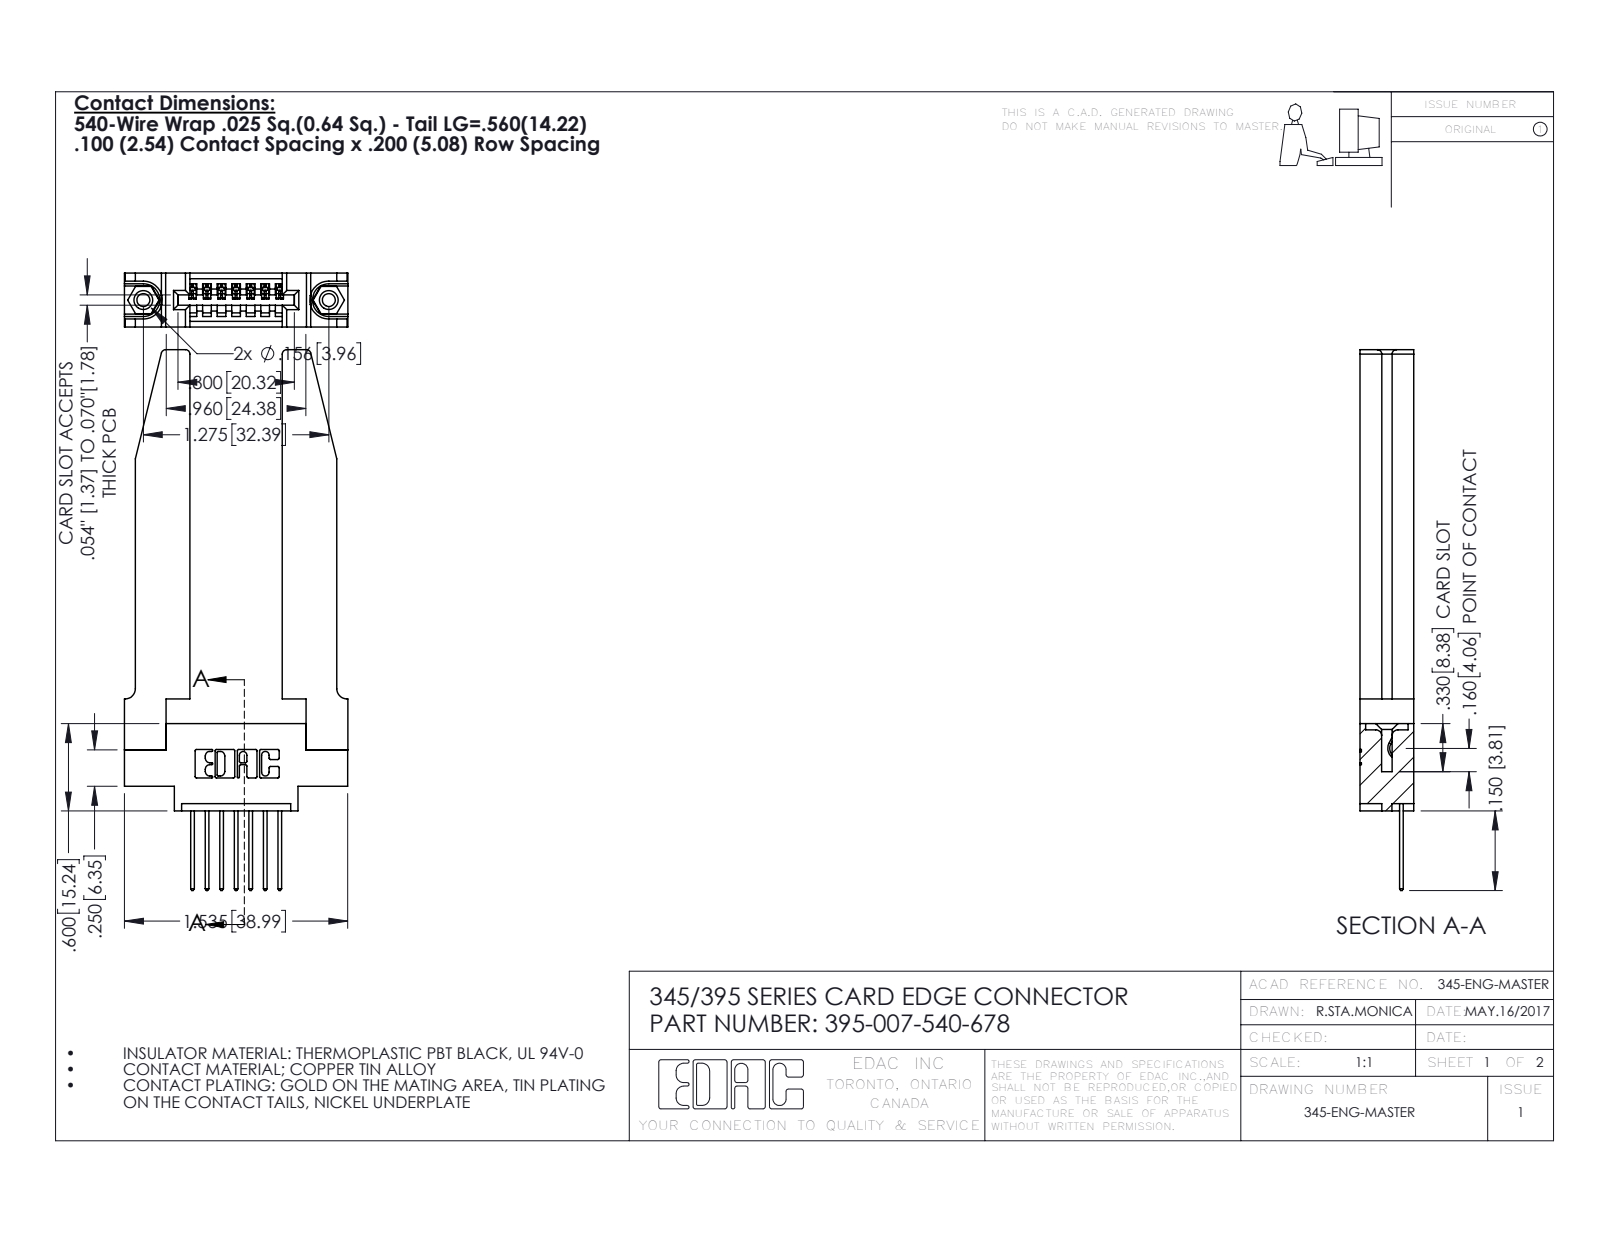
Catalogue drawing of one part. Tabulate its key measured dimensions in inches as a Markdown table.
| quantity | value |
| --- | --- |
| part name | 345-250-001_345-250-001-102; 345-292-001_345-293-140; 345-220-078_345-220-078; 345 Part_0.170 Offset - 0.156 Dia-TH (+1 more) |
| STEP written by | SolidWorks 2016 (CONFIG_CONTROL_DESIGN) |
| units | inches |
| bodies | 12 solids, 770 faces (506 planar, 212 cylindrical, 52 other) |
| overall size | 3.717 × 1.536 × 0.37 |
| volume | 0.676 in³ |
| surface area | 17 in² |
| round holes (diameter × count) | 0.089 × 2, 0.125 × 2, 0.156 × 2, 0.064 × 1 |
| round bosses / shafts (diameter × count) | 0.155 × 2 |
| partial cylindrical surfaces (radius × count) | 0.01 × 22, 0.006 × 14, 0.01 × 14, 0.03 × 8, 0.007 × 6, 0.031 × 6, 0.026 × 3, 0.031 × 2 |
| main face-to-face distances | 0.37, 0.15, 0.072, 0.22, 0.298, 0.148, 0.635, 0.077, 0.095, 0.2 |
| hole center spacings | 0.27, 1.045, 1.275 |
